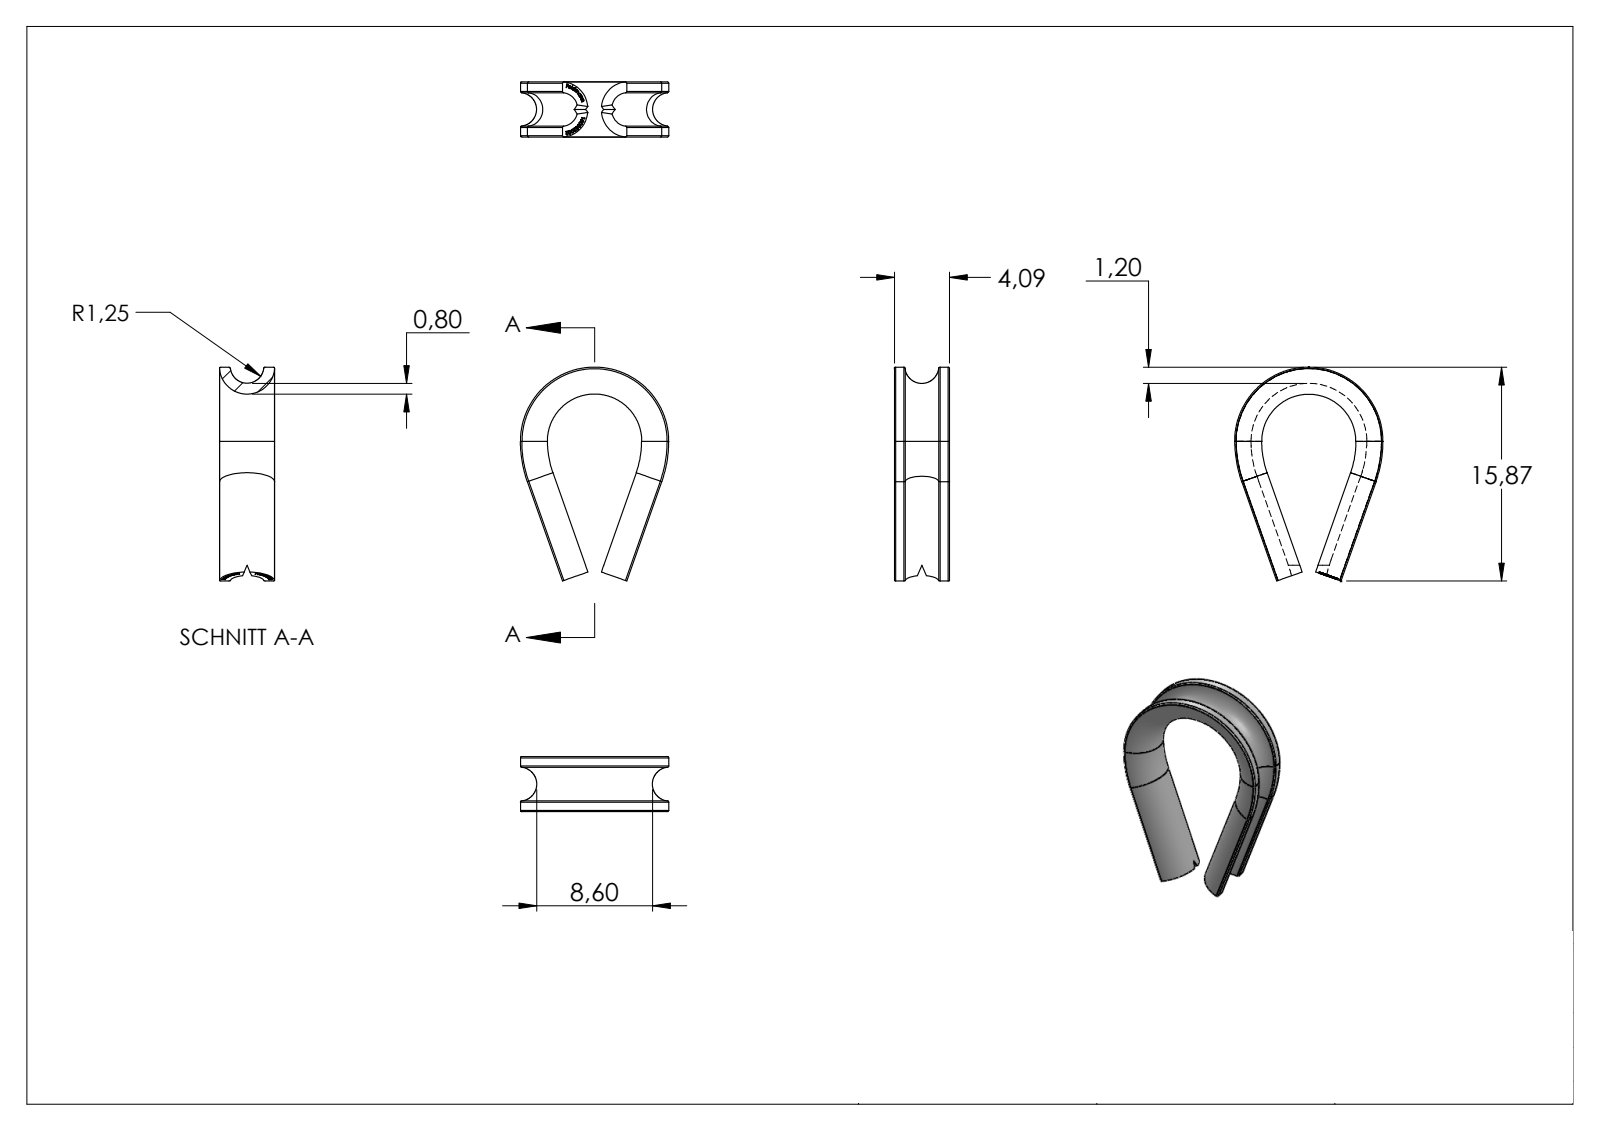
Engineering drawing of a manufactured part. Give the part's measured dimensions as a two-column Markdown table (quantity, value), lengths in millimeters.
| quantity | value |
| --- | --- |
| part name | 100052002 |
| STEP written by | SolidWorks 2015 (CONFIG_CONTROL_DESIGN) |
| units | millimeters |
| bodies | 1 solid, 272 faces (115 planar, 20 cylindrical, 137 other) |
| overall size | 15.87 × 11 × 4.09 |
| volume | 142 mm³ |
| surface area | 421 mm² |
| partial cylindrical surfaces (radius × count) | 0.1 × 8, 1.25 × 2, 2.05 × 2, 9 × 2, 5.5 × 1 |
